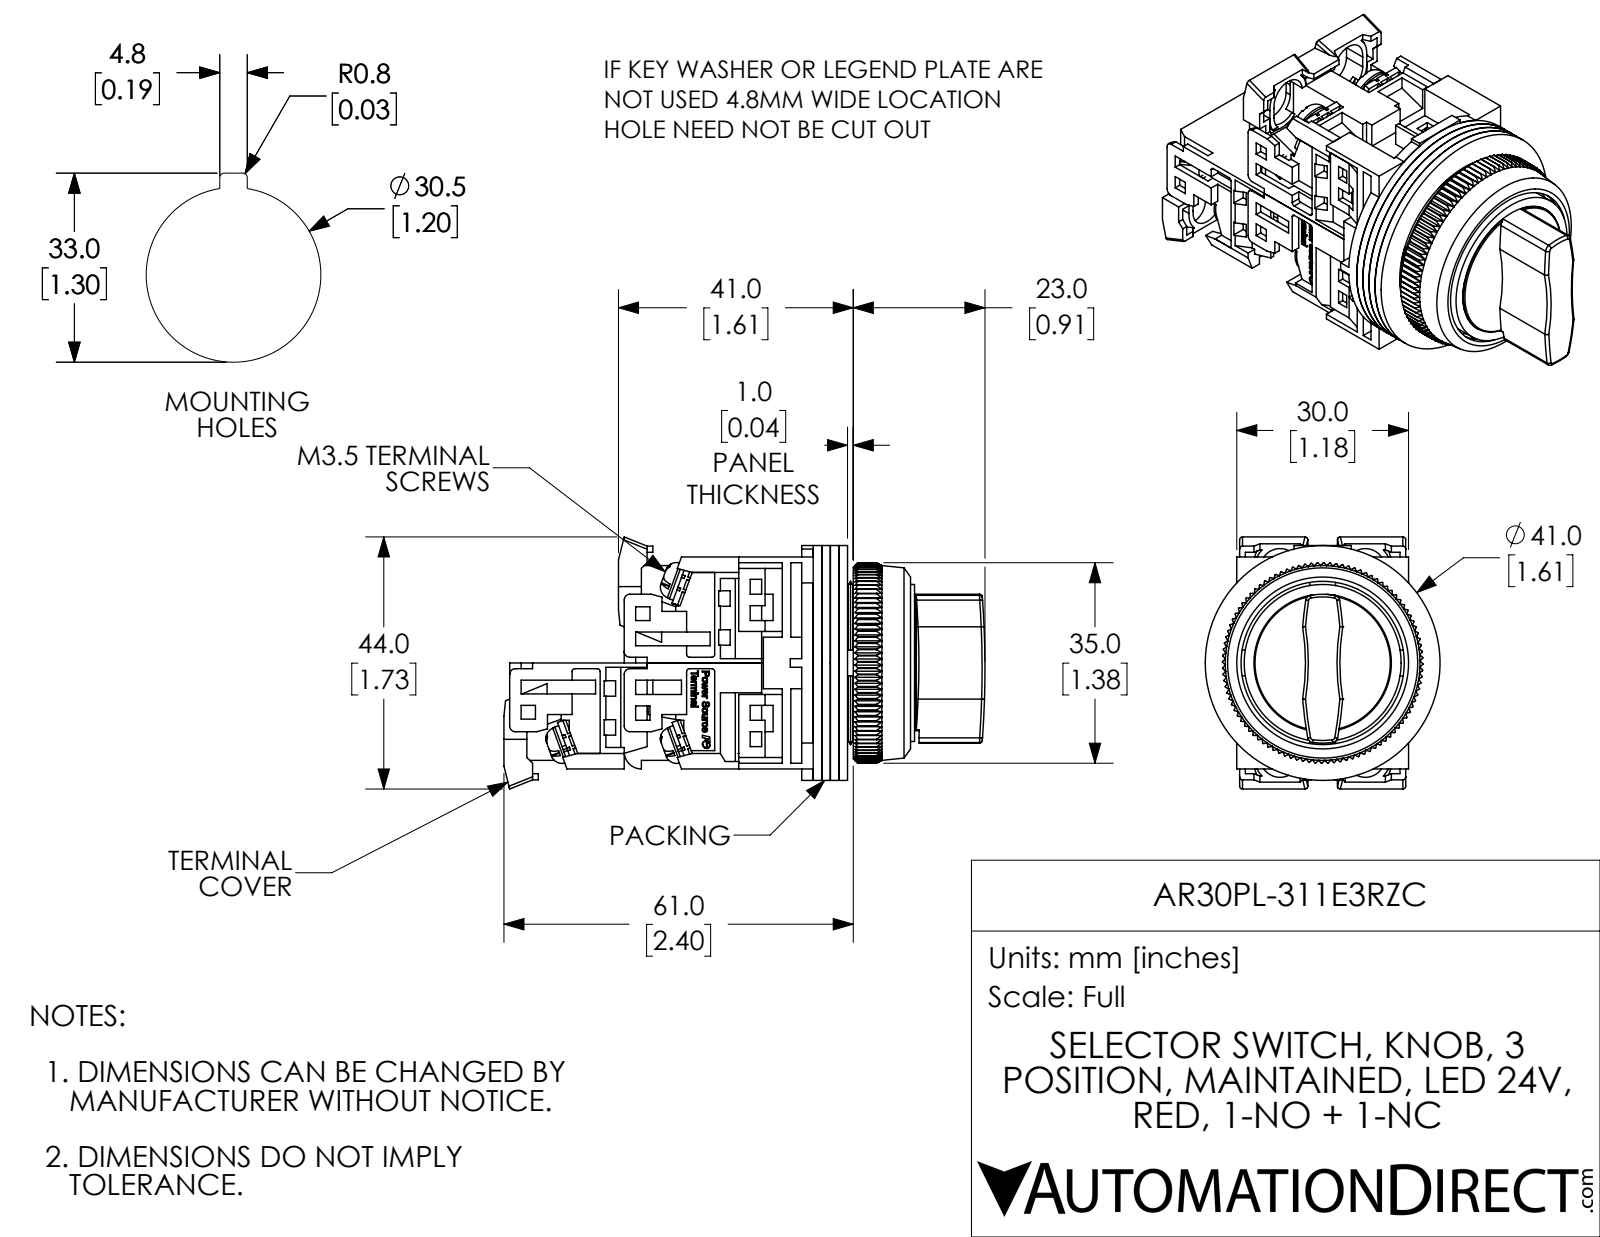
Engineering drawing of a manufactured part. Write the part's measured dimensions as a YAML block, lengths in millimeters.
part_name: "AR30PL-311E3RZC"
step_written_by: "SolidWorks 2017 (AUTOMOTIVE_DESIGN)"
units: millimeters
bodies: {solids: 32, faces: 2783, planar: 2039, cylindrical: 338, other: 406}
overall_size: [84, 44, 41]
volume: 43870
surface_area: 42930
round_holes:
  - {diameter: 3.5, count: 10}
  - {diameter: 3.6, count: 6}
  - {diameter: 3, count: 1}
  - {diameter: 12, count: 1}
  - {diameter: 18, count: 1}
  - {diameter: 19.5, count: 1}
  - {diameter: 21, count: 1}
  - {diameter: 28.5, count: 1}
  - {diameter: 30, count: 1}
  - {diameter: 31.8, count: 1}
round_bosses_or_shafts:
  - {diameter: 6.6, count: 6}
  - {diameter: 3.5, count: 6}
  - {diameter: 1.6, count: 2}
  - {diameter: 41, count: 1}
  - {diameter: 29.2, count: 1}
  - {diameter: 27.4, count: 1}
  - {diameter: 24, count: 1}
  - {diameter: 22.5, count: 1}
partial_cylinders:
  - {radius: 1.5, count: 24}
  - {radius: 0.5, count: 14}
  - {radius: 1, count: 10}
  - {radius: 3.5, count: 4}
  - {radius: 4.5, count: 4}
  - {radius: 3, count: 3}
  - {radius: 40, count: 2}
  - {radius: 75, count: 2}
face_to_face_distances: [1.5, 3, 4.5, 1, 20, 1.6, 2, 0.5, 20.6, 17.5]
hole_center_spacings: [14.7, 6.8, 16.2, 15.5]
